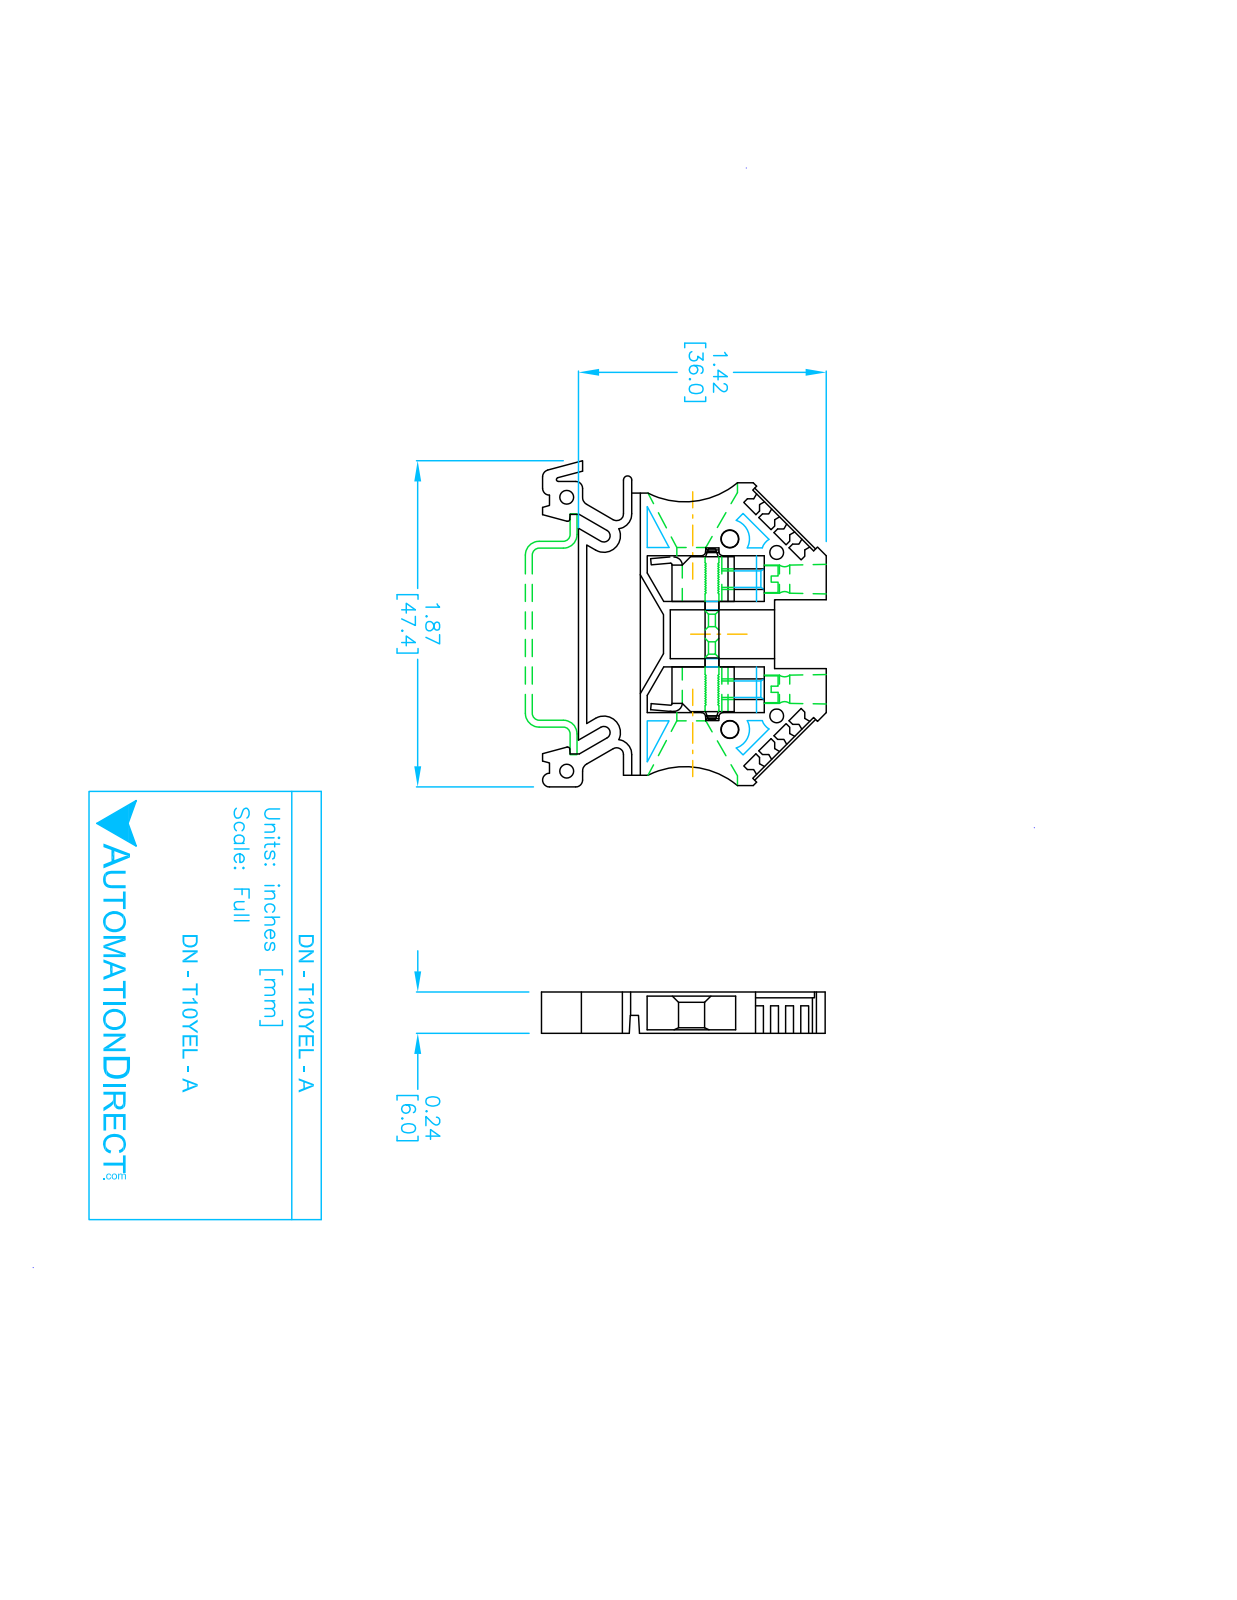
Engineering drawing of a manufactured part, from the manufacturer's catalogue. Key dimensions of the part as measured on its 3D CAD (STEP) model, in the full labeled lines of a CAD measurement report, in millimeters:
Part name (STEP PRODUCT): DN-T10YEL-A
STEP written by: SolidWorks 2017 (AUTOMOTIVE_DESIGN)
Units: millimetres
Bodies: 1 solid, 181 faces (141 planar, 40 cylindrical, 0 other)
Overall size (bounding box): 47.4 × 41.2 × 6
Volume: 6 240 mm³ · Surface area: 4 957 mm²
Round holes (diameter × count): ⌀2 ×2, ⌀4.4 ×2
Partial cylindrical surfaces — rounded edges, fillets, slot ends (radius × count): R1 ×7, R0.3 ×2, R0.9 ×2, R1.2 ×2, R2.2 ×2, R2.4 ×2, R12 ×2, R0.3 ×1
Main face-to-face distances: 5.8, 6, 3.6, 2.4, 1.2, 2.2, 3.4, 9, 1.8, 7.8
Hole centre spacings: 16, 39.8
